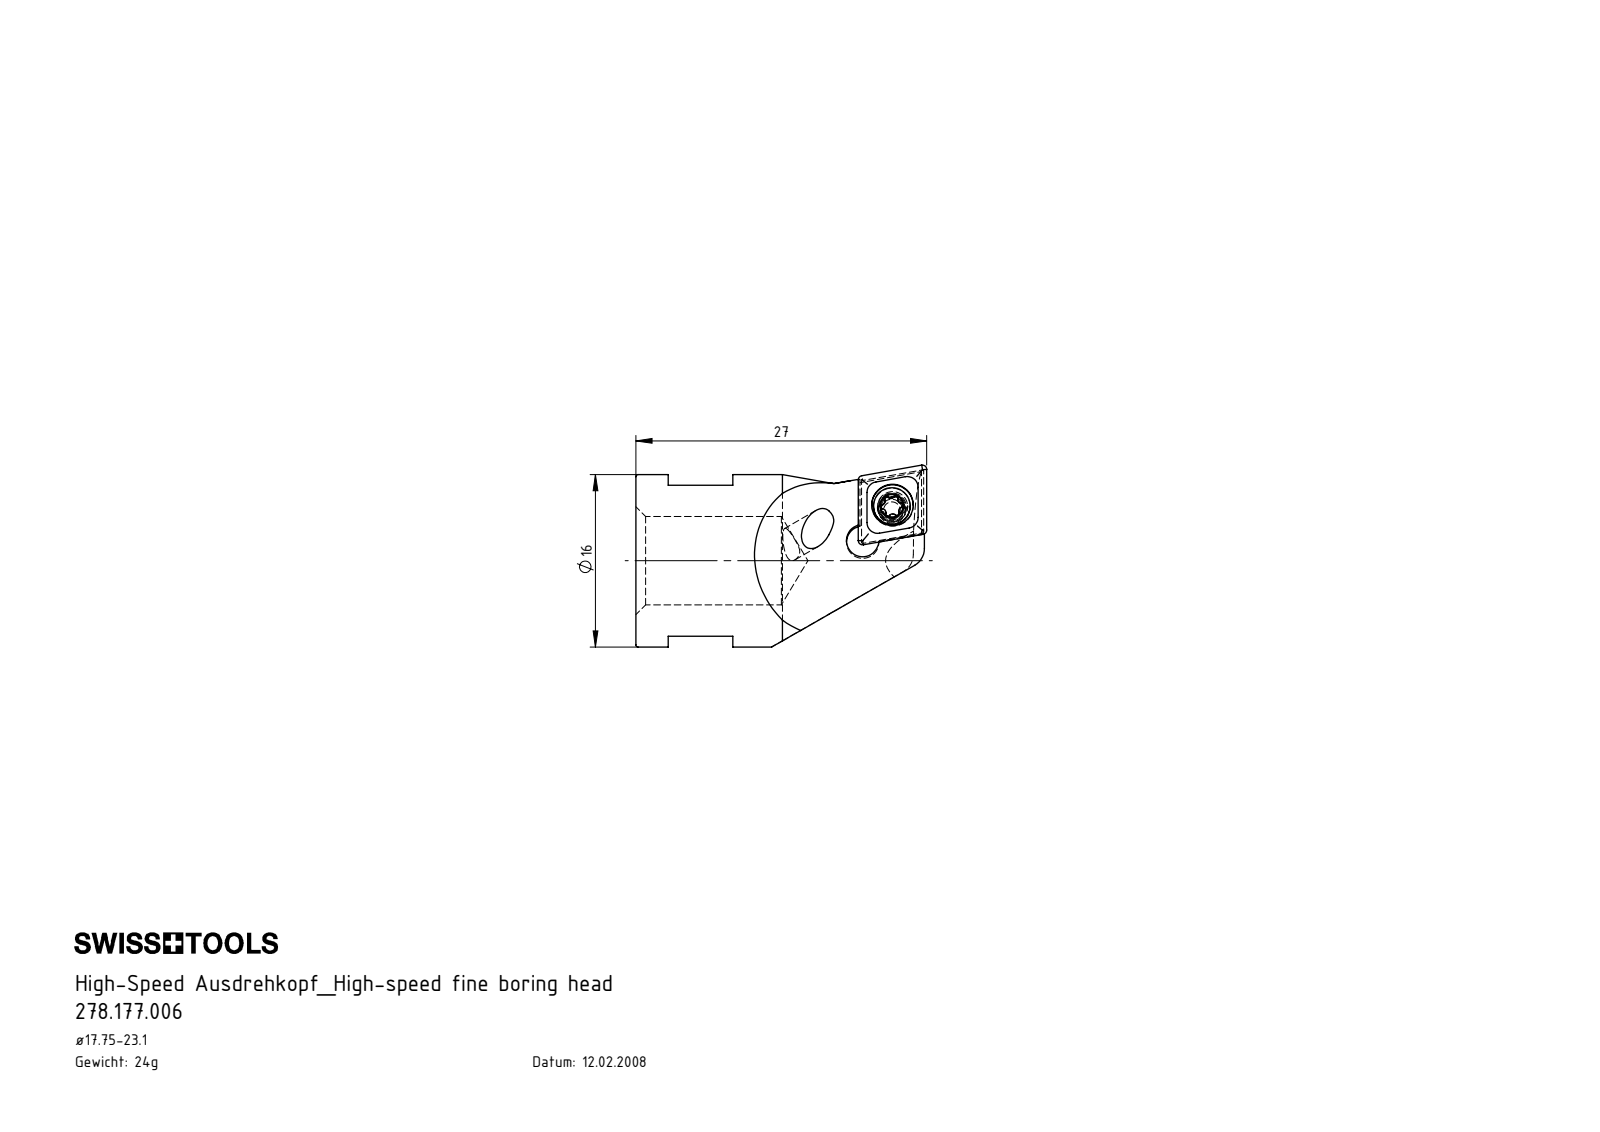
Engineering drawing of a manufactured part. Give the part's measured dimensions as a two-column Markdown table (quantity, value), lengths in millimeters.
| quantity | value |
| --- | --- |
| part name | HS0-A18.K11.027; HS0-A18.K11.027_A; CCMT060204; WCA-ER2.001.006_A |
| STEP written by | SolidWorks 2015 (AUTOMOTIVE_DESIGN) |
| units | millimeters |
| bodies | 3 solids, 133 faces (39 planar, 40 cylindrical, 54 other) |
| overall size | 27 × 16.88 × 16 |
| volume | 3 008 mm³ |
| surface area | 2 059 mm² |
| round holes (diameter × count) | 2.05 × 1, 2.8 × 1, 3 × 1, 3.85 × 1, 8.2 × 1 |
| round bosses / shafts (diameter × count) | 16 × 1, 3.4 × 1, 2.5 × 1 |
| partial cylindrical surfaces (radius × count) | 0.21 × 6, 0.36 × 5, 1 × 4, 0.36 × 1, 1.5 × 1, 1.8 × 1, 2 × 1 |
| main face-to-face distances | 14.01, 2.28, 6, 2.38, 9, 3, 2.48, 2.58, 20.8, 17.8 |
